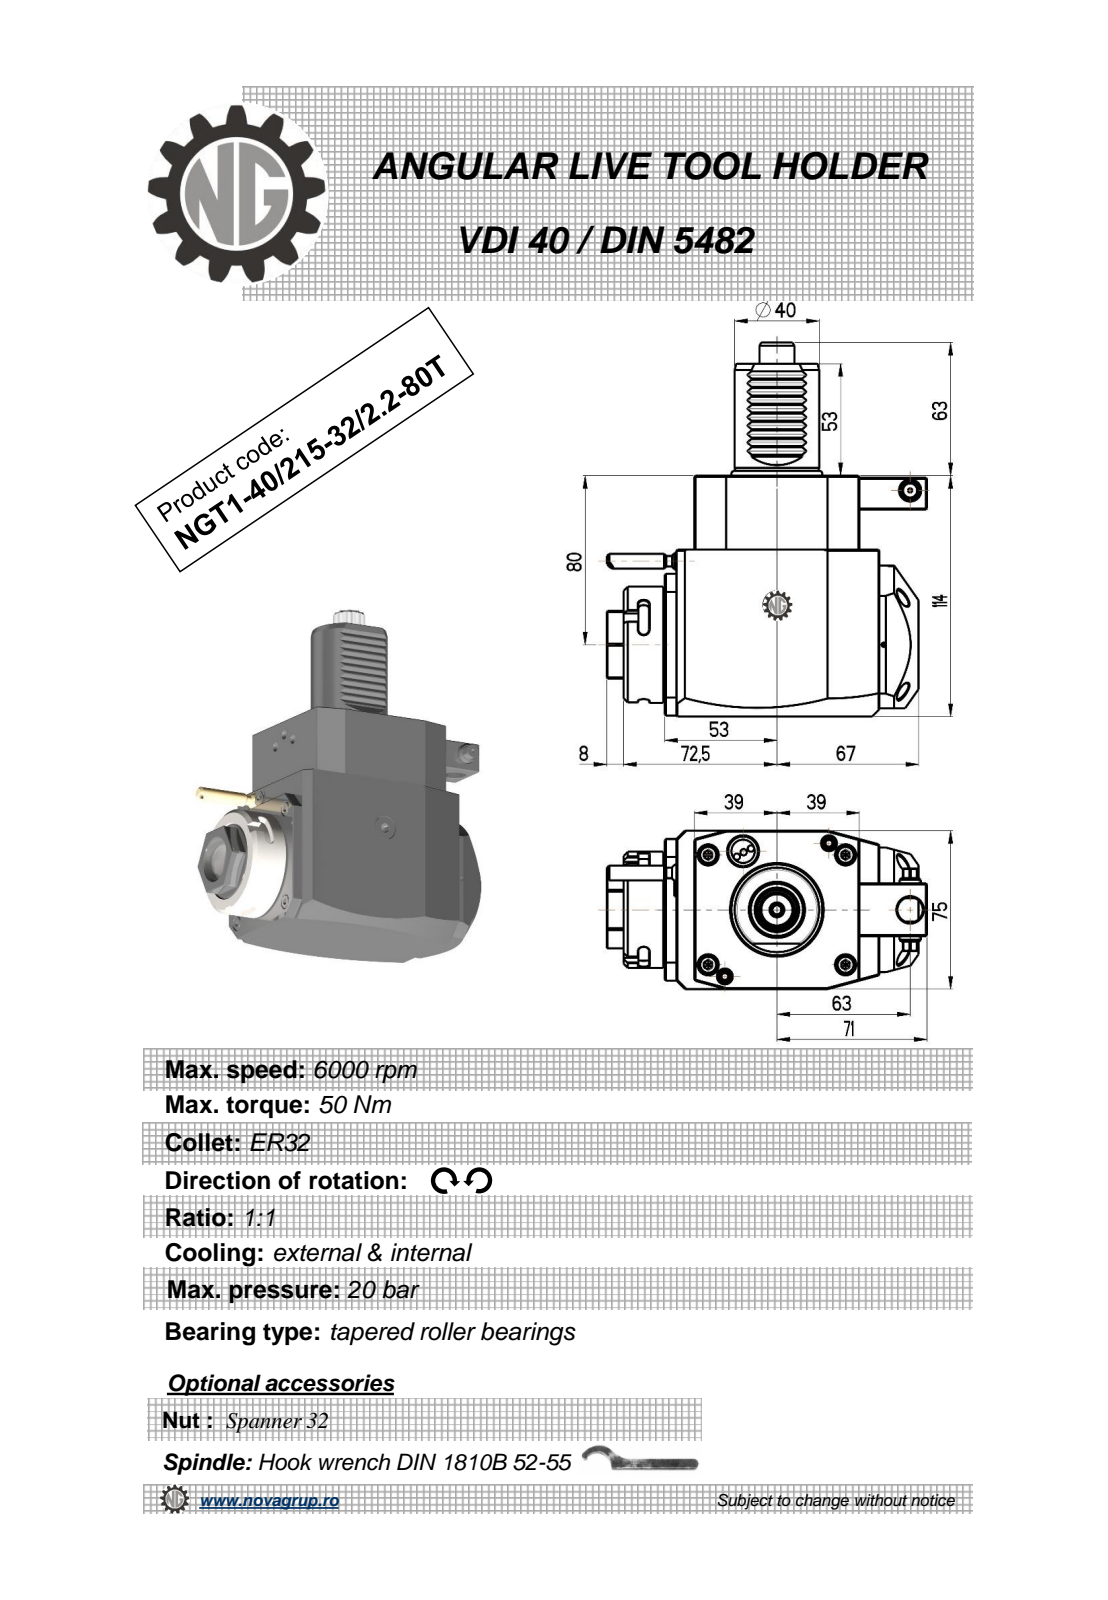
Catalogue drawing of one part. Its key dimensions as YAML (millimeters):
part_name: "NGT1_40_215_32_1_2_80T"
step_written_by: "PRO/ENGINEER BY PARAMETRIC TECHNOLOGY CORPORATION, 2010280 (CONFIG_CONTROL_DESIGN)"
units: millimeters
bodies: {solids: 1, faces: 390, planar: 182, cylindrical: 117, other: 91}
overall_size: [177, 151.5, 75]
volume: 952929
surface_area: 71166
round_holes:
  - {diameter: 2, count: 1}
  - {diameter: 2.5, count: 1}
  - {diameter: 3, count: 1}
  - {diameter: 4.2, count: 1}
  - {diameter: 5.3, count: 1}
  - {diameter: 9.5, count: 1}
  - {diameter: 12, count: 1}
  - {diameter: 23, count: 1}
round_bosses_or_shafts:
  - {diameter: 8, count: 2}
  - {diameter: 55, count: 1}
  - {diameter: 48, count: 1}
  - {diameter: 40, count: 1}
  - {diameter: 10, count: 1}
  - {diameter: 7, count: 1}
  - {diameter: 5, count: 1}
partial_cylinders:
  - {radius: 3.03, count: 18}
  - {radius: 0.3, count: 10}
  - {radius: 2.5, count: 6}
  - {radius: 180, count: 2}
  - {radius: 0.5, count: 1}
  - {radius: 3.85, count: 1}
  - {radius: 4.25, count: 1}
  - {radius: 6.75, count: 1}
face_to_face_distances: [75, 114, 14, 92, 78, 25, 19.5, 33.5, 111.5, 4]
hole_center_spacings: [37.35, 43.2, 63, 72.5]
